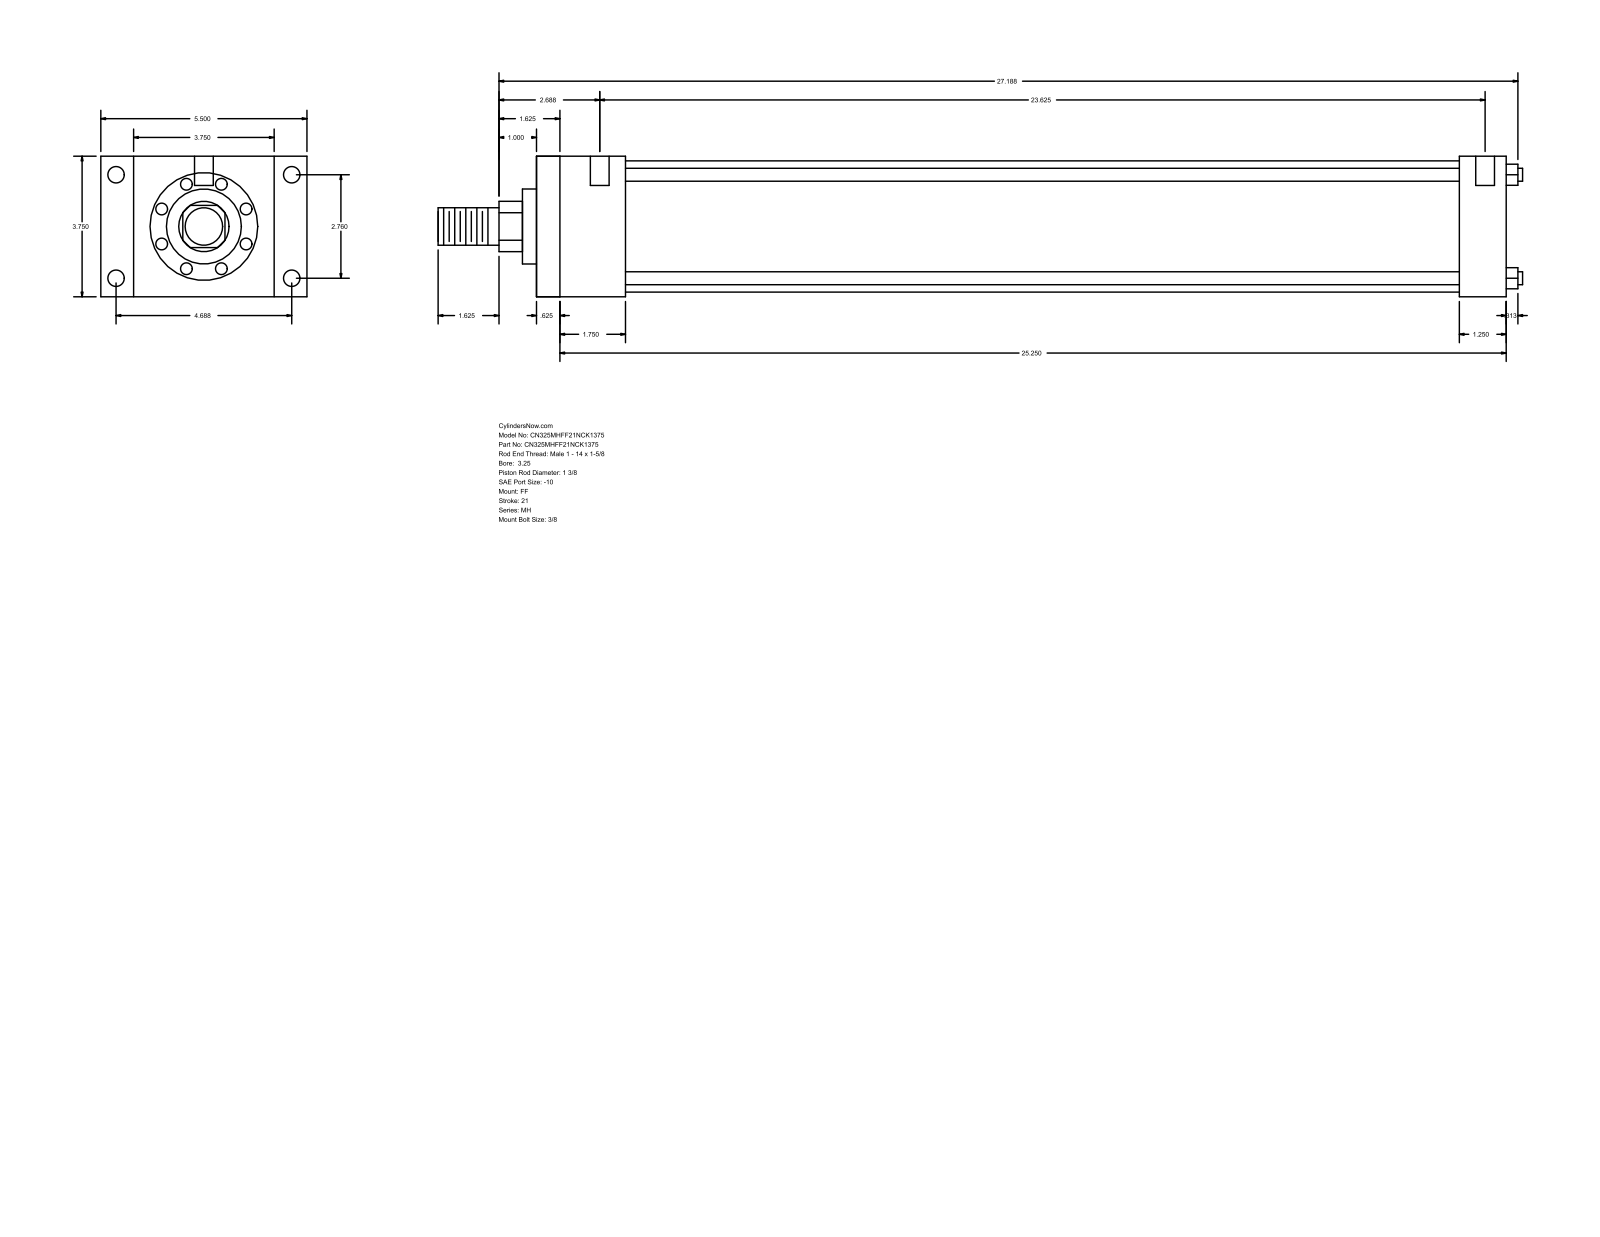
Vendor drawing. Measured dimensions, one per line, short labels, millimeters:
name: MH_FF__0325_1.375
written by: GSSL Pune (CONFIG_CONTROL_DESIGN)
unit: mm
bodies: 0 solids, 92 faces (64 planar, 28 cylindrical, 0 other)
size: 735.01 × 139.7 × 95.25
holes: 4× ⌀5.56, 4× ⌀11.13, 2× ⌀12.7
bosses: 4× ⌀8.76, 1× ⌀88.9, 1× ⌀50.8, 1× ⌀34.92, 1× ⌀25.4
rounds: 1× R17.06
face distances: 95.24, 657.22, 15.87, 641.35, 22.23, 117.47, 625.48, 609.61, 31.74, 60.32
hole spacings: 70.1, 119.06, 138.16, 606.43, 1.59, 4.76, 600.08, 601.67
